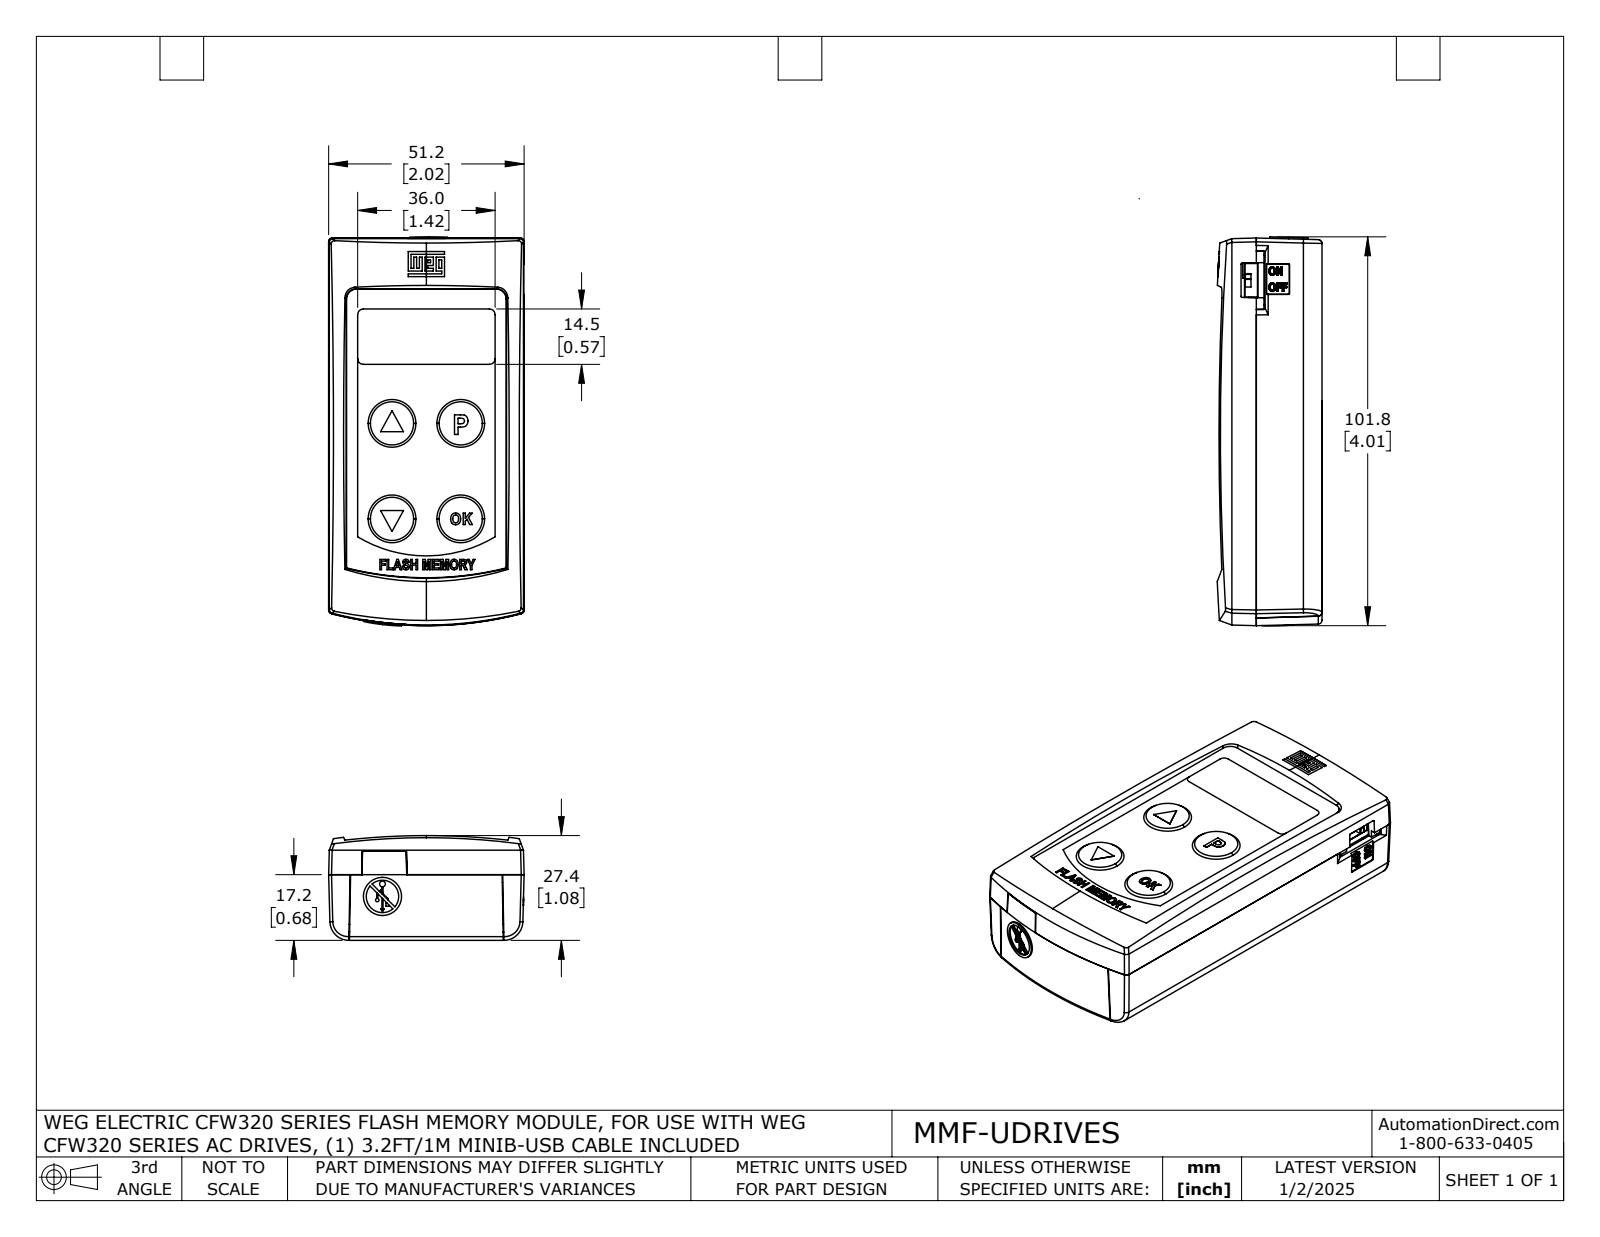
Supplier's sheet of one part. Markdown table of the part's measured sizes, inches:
| quantity | value |
| --- | --- |
| part name | MMF-UDRIVES |
| STEP written by | SolidWorks 2021 (AUTOMOTIVE_DESIGN) |
| units | inches |
| bodies | 9 solids, 1756 faces (1059 planar, 280 cylindrical, 417 other) |
| overall size | 4.01 × 2.016 × 1.08 |
| volume | 2.812 in³ |
| surface area | 87.21 in² |
| round holes (diameter × count) | 0.079 × 2 |
| round bosses / shafts (diameter × count) | 0.031 × 2, 0.028 × 2 |
| partial cylindrical surfaces (radius × count) | 0.012 × 110, 0.004 × 27, 0.031 × 19, 0.03 × 16, 0.039 × 15, 0.118 × 6, 0.197 × 6, 0.008 × 4 |
| main face-to-face distances | 0.063, 0.343, 0.406, 0.079, 0.598, 0.661, 0.52, 0.583, 0.925, 1.004 |
| hole center spacings | 3.359 |
